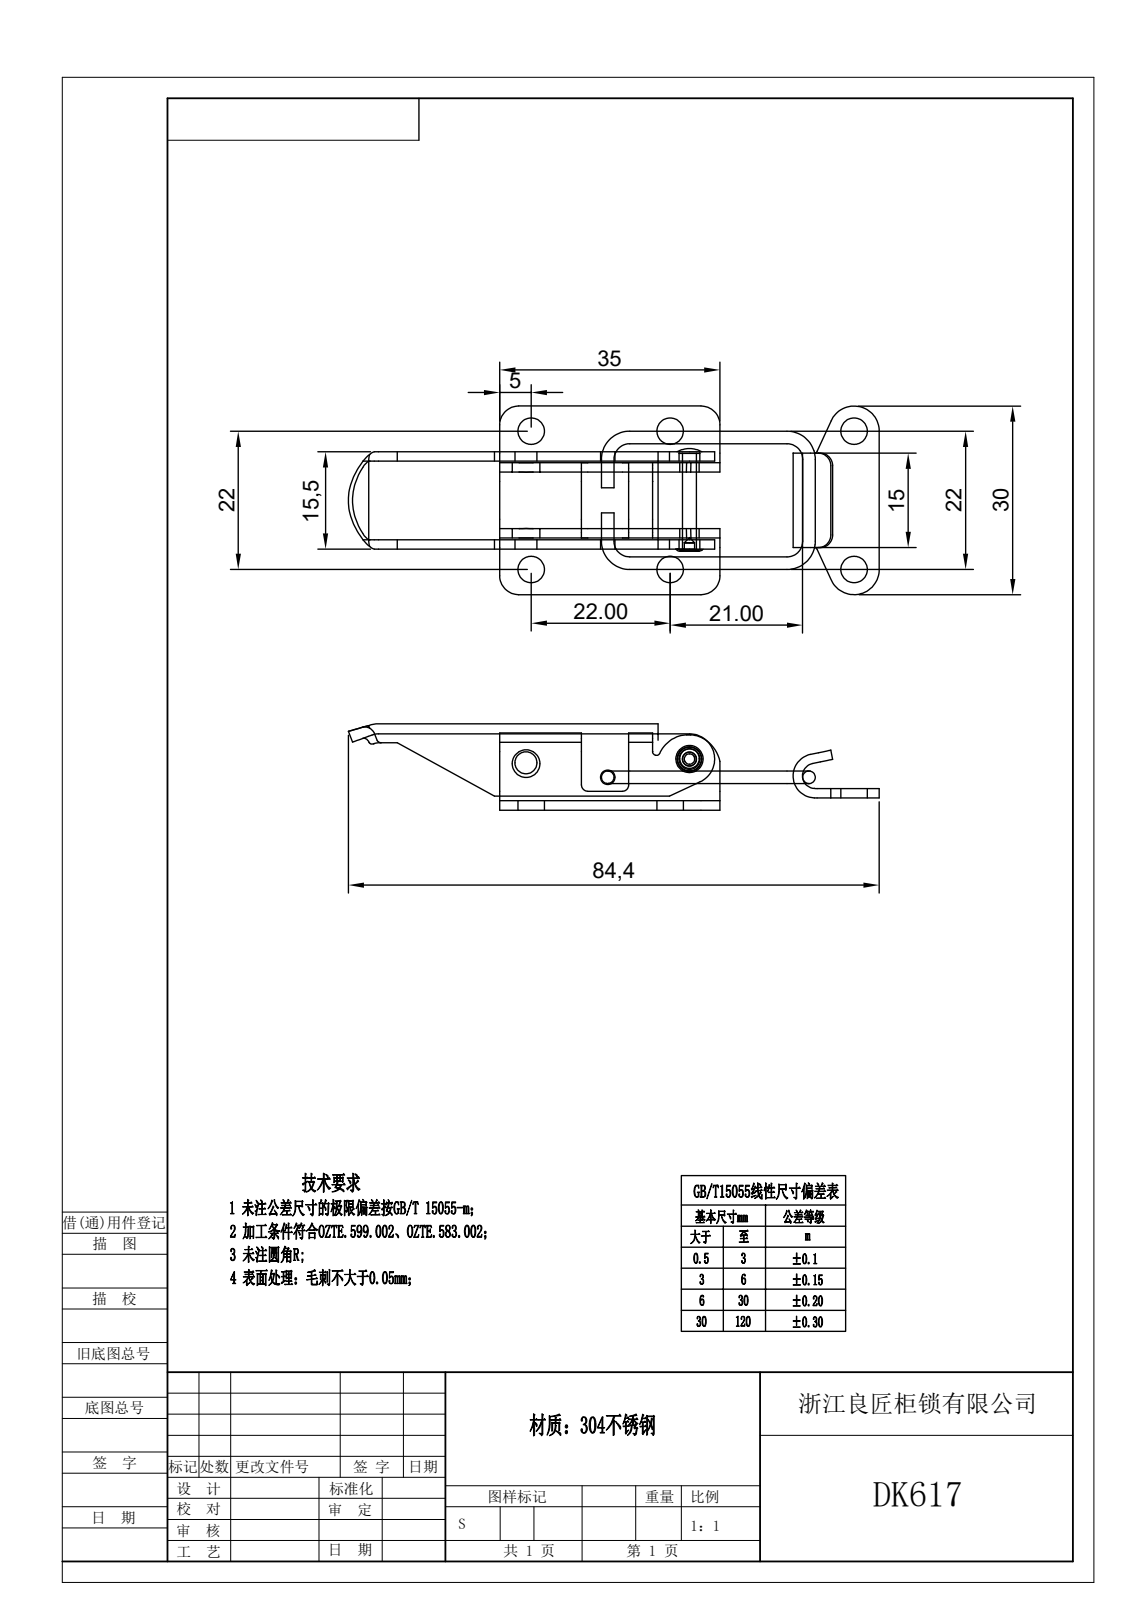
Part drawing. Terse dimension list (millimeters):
name: DK617_id6_x_t
written by: Rhino 8.5 (CONFIG_CONTROL_DESIGN)
unit: mm
bodies: 5 solids, 203 faces (74 planar, 92 cylindrical, 37 other)
size: 84.4 × 30 × 13.73
volume: 5 233 mm³; area: 8 156 mm²
holes: 6× ⌀4.2, 1× ⌀2.3, 1× ⌀3.1, 1× ⌀3.3, 1× ⌀3.5, 1× ⌀4.4
bosses: 4× ⌀2, 1× ⌀2.21
rounds: 10× R3, 6× R1, 6× R1.5, 3× R2, 3× R4, 2× R0.5, 1× R0.82, 1× R0.83
face distances: 1.5, 14, 1.6, 1.95, 10.64, 12.24, 12.14, 13.74, 10.5, 15.5
hole spacings: 22, 22.09, 25.99, 26.01, 29.24, 31.18, 36.59, 51.33
